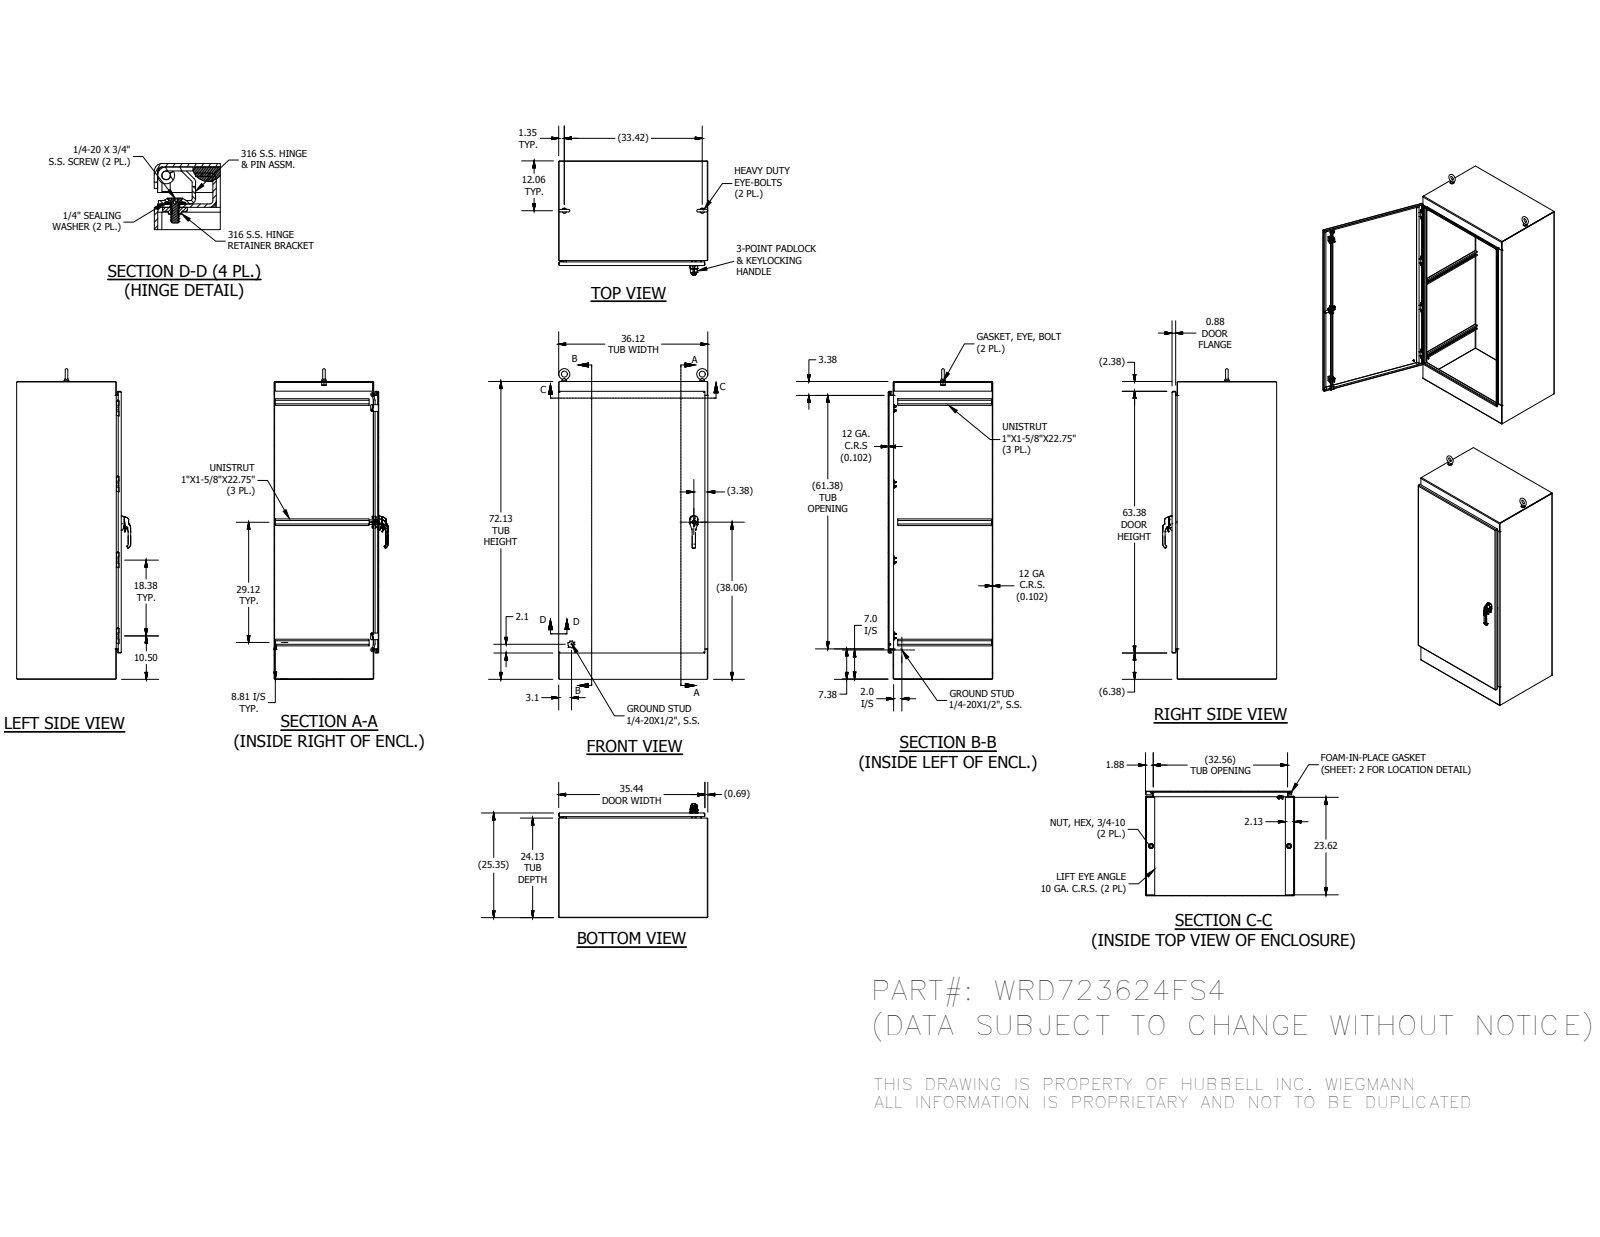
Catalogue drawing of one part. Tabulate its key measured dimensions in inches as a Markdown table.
| quantity | value |
| --- | --- |
| part name | WRD723624FS4BLR; WRD3624FS4TOP; WRD3624FS4BTM; WRD7236FS4DR (+8 more) |
| STEP written by | Autodesk Inventor 2016 (AUTOMOTIVE_DESIGN) |
| units | inches |
| bodies | 85 solids, 3586 faces (1457 planar, 1207 cylindrical, 922 other) |
| overall size | 75.248 × 36.127 × 27.616 |
| volume | 1 292 in³ |
| surface area | 24 740 in² |
| round holes (diameter × count) | 0.23 × 8, 0.276 × 8, 0.281 × 8, 0.65 × 8, 0.2 × 4, 0.213 × 3, 0.236 × 3, 0.28 × 3, 0.241 × 2, 0.25 × 2, 0.252 × 2, 0.4 × 2 |
| round bosses / shafts (diameter × count) | 0.25 × 15, 0.625 × 8, 0.404 × 8, 0.182 × 8, 1.25 × 2, 1.12 × 2, 1 × 2, 0.75 × 2 |
| partial cylindrical surfaces (radius × count) | 0.02 × 164, 0.012 × 86, 0.063 × 27, 0.01 × 24, 0.125 × 20, 0.019 × 19, 0.079 × 15, 0.05 × 14 |
| main face-to-face distances | 0.102, 25.245, 36.023, 25.143, 25.347, 35.921, 72.023, 36.125, 24.023, 1.222 |
| hole center spacings | 0.492, 1, 18.375, 36.75, 0.256, 0.886, 2.028, 0.236 |
